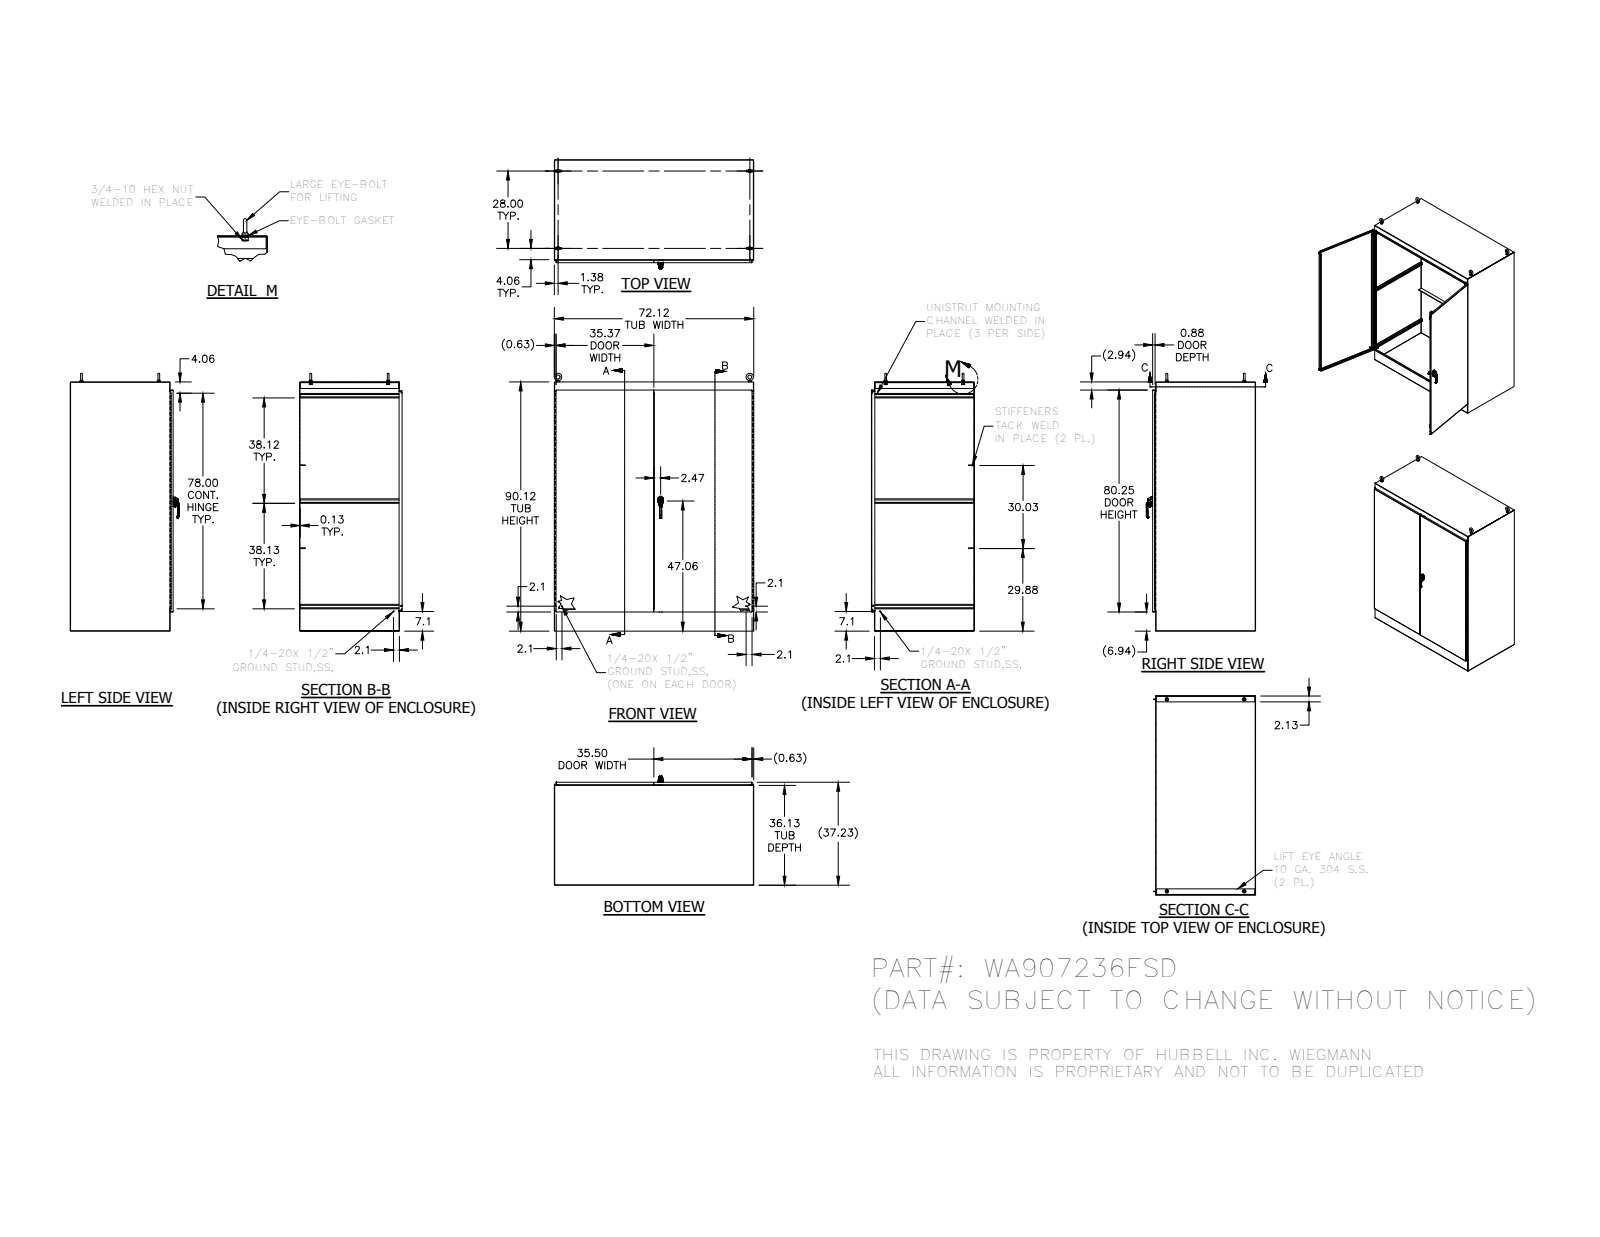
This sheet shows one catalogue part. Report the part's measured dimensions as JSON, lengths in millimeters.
{"part_name": "FUN00105; HFW3025; 316298; 349132 (+8 more)", "step_written_by": "Autodesk Inventor 2014 (AUTOMOTIVE_DESIGN)", "units": "millimeters", "bodies": {"solids": 72, "faces": 3890, "planar": 1791, "cylindrical": 1269, "other": 830}, "overall_size": [2368.49, 1832.09, 1003.25], "volume_mm3": 57590000, "surface_area_mm2": 36330000, "round_holes": [[9.52, 16], [7.02, 8], [5.08, 4], [16.31, 4], [20.64, 4], [5.4, 3], [6, 3], [7.11, 3], [3.61, 2], [4.57, 2], [6.13, 2], [6.35, 2]], "round_bosses_or_shafts": [[31.75, 4], [28.45, 4], [19.05, 4], [8.56, 3], [6.35, 3], [25.4, 2], [14.29, 2], [13.37, 2]], "partial_cylinders_radius": [[0.5, 166], [0.3, 89], [0.79, 24], [3.97, 21], [3.17, 20], [0.47, 19], [0.25, 16], [2, 15]], "face_to_face_distances": [3.18, 1828.8, 3.17, 942.46, 939.28, 945.63, 942.45, 2286, 1825.62, 1831.98], "hole_center_spacings": [220.13, 660.4, 440.27, 1798.26, 1804.99, 1818.36, 880.53, 1838.24]}
